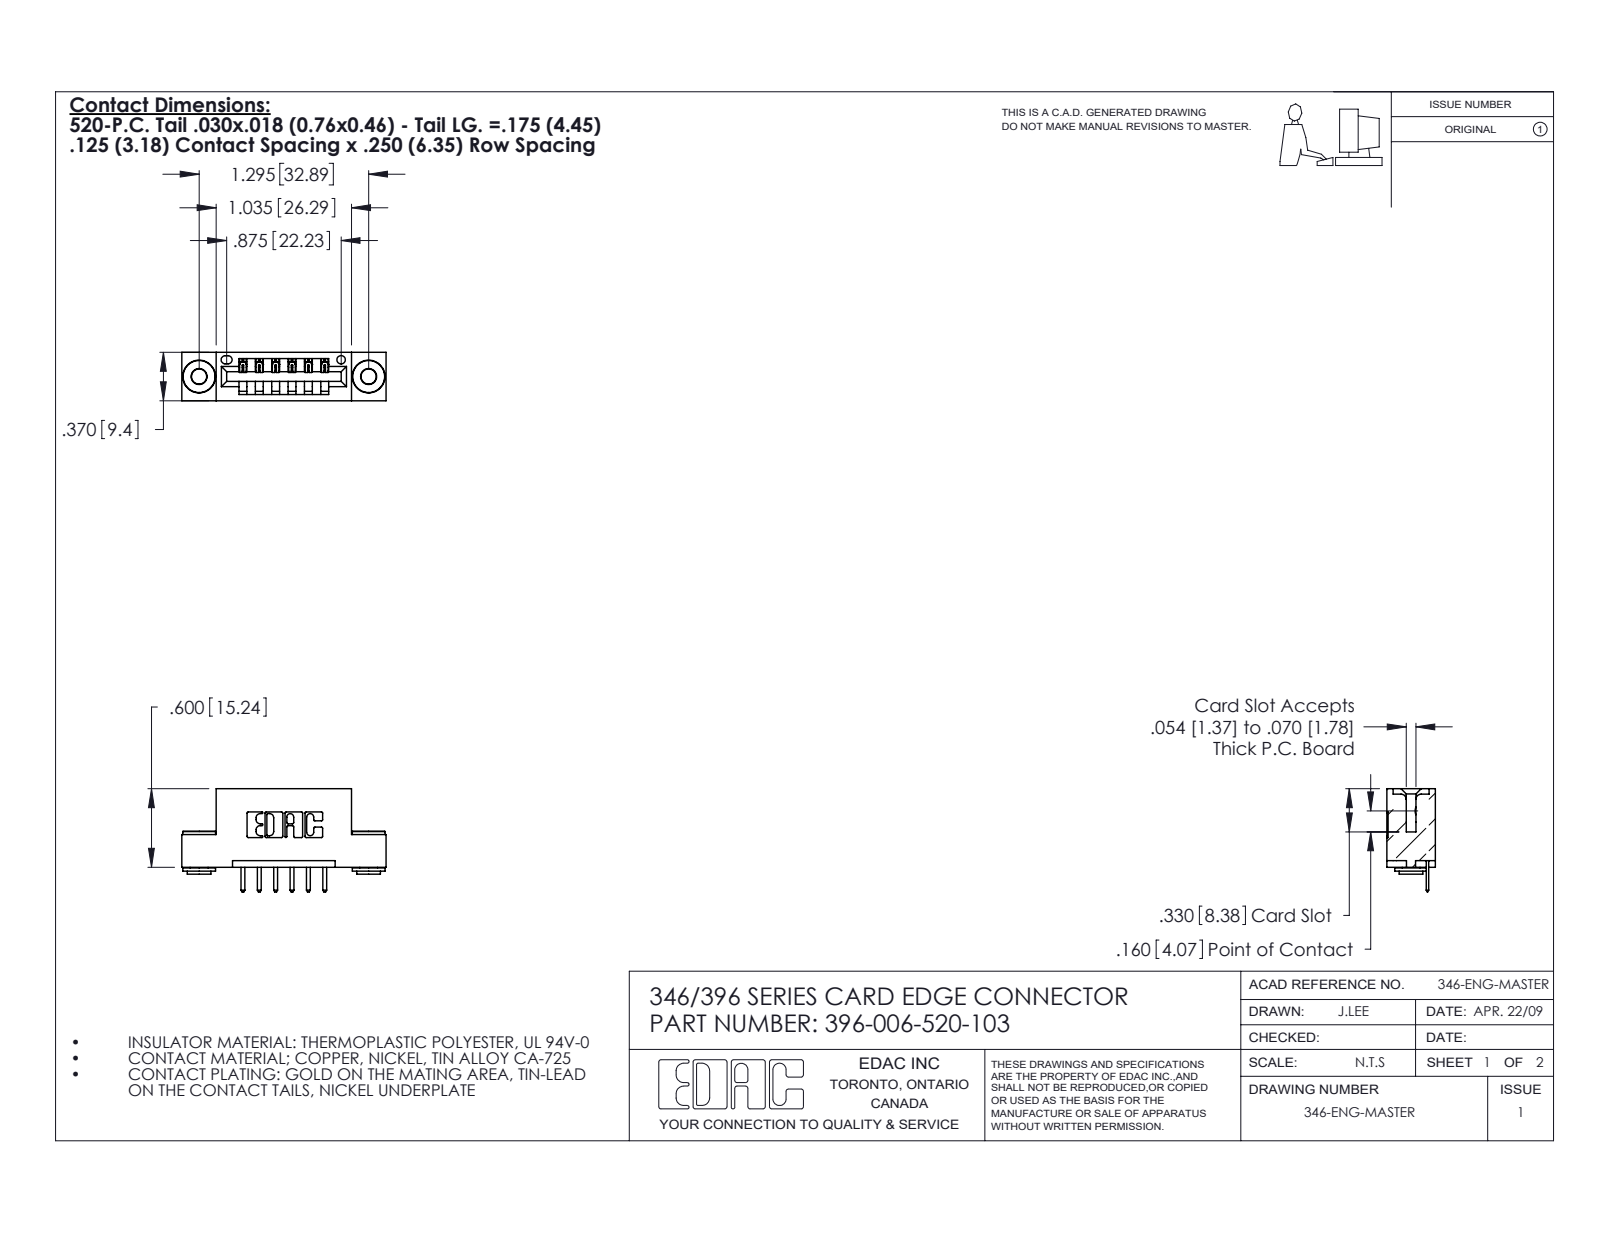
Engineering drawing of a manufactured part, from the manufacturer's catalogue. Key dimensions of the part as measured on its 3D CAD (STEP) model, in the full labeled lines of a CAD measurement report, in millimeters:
Part name (STEP PRODUCT): 396-006-520-103; 345-292-001_345-293-120; 346 Part_Flush Mounting Lugs - 0.156 Dia-TH; 345-250-002_345-250-002-102
STEP written by: SolidWorks 2020 (CONFIG_CONTROL_DESIGN)
Units: millimetres
Bodies: 9 solids, 546 faces (352 planar, 186 cylindrical, 8 other)
Overall size (bounding box): 39.6 × 20 × 9.4
Volume: 3 520 mm³ · Surface area: 4 216 mm²
Round holes (diameter × count): ⌀2.9 ×2, ⌀4 ×2, ⌀1.6 ×1
Round bosses / shafts (diameter × count): ⌀6.4 ×2, ⌀4.6 ×2, ⌀3.5 ×2
Partial cylindrical surfaces — rounded edges, fillets, slot ends (radius × count): R0.3 ×22, R0.3 ×14, R0.2 ×12, R0.2 ×6, R0.8 ×6, R0.7 ×3, R0.8 ×2, R1 ×2
Main face-to-face distances: 6.4, 9.4, 1.2, 8.2, 3.8, 5.6, 2.5, 4.4, 3.2, 3.2
Hole centre spacings: 6.2, 27.7, 32.9
